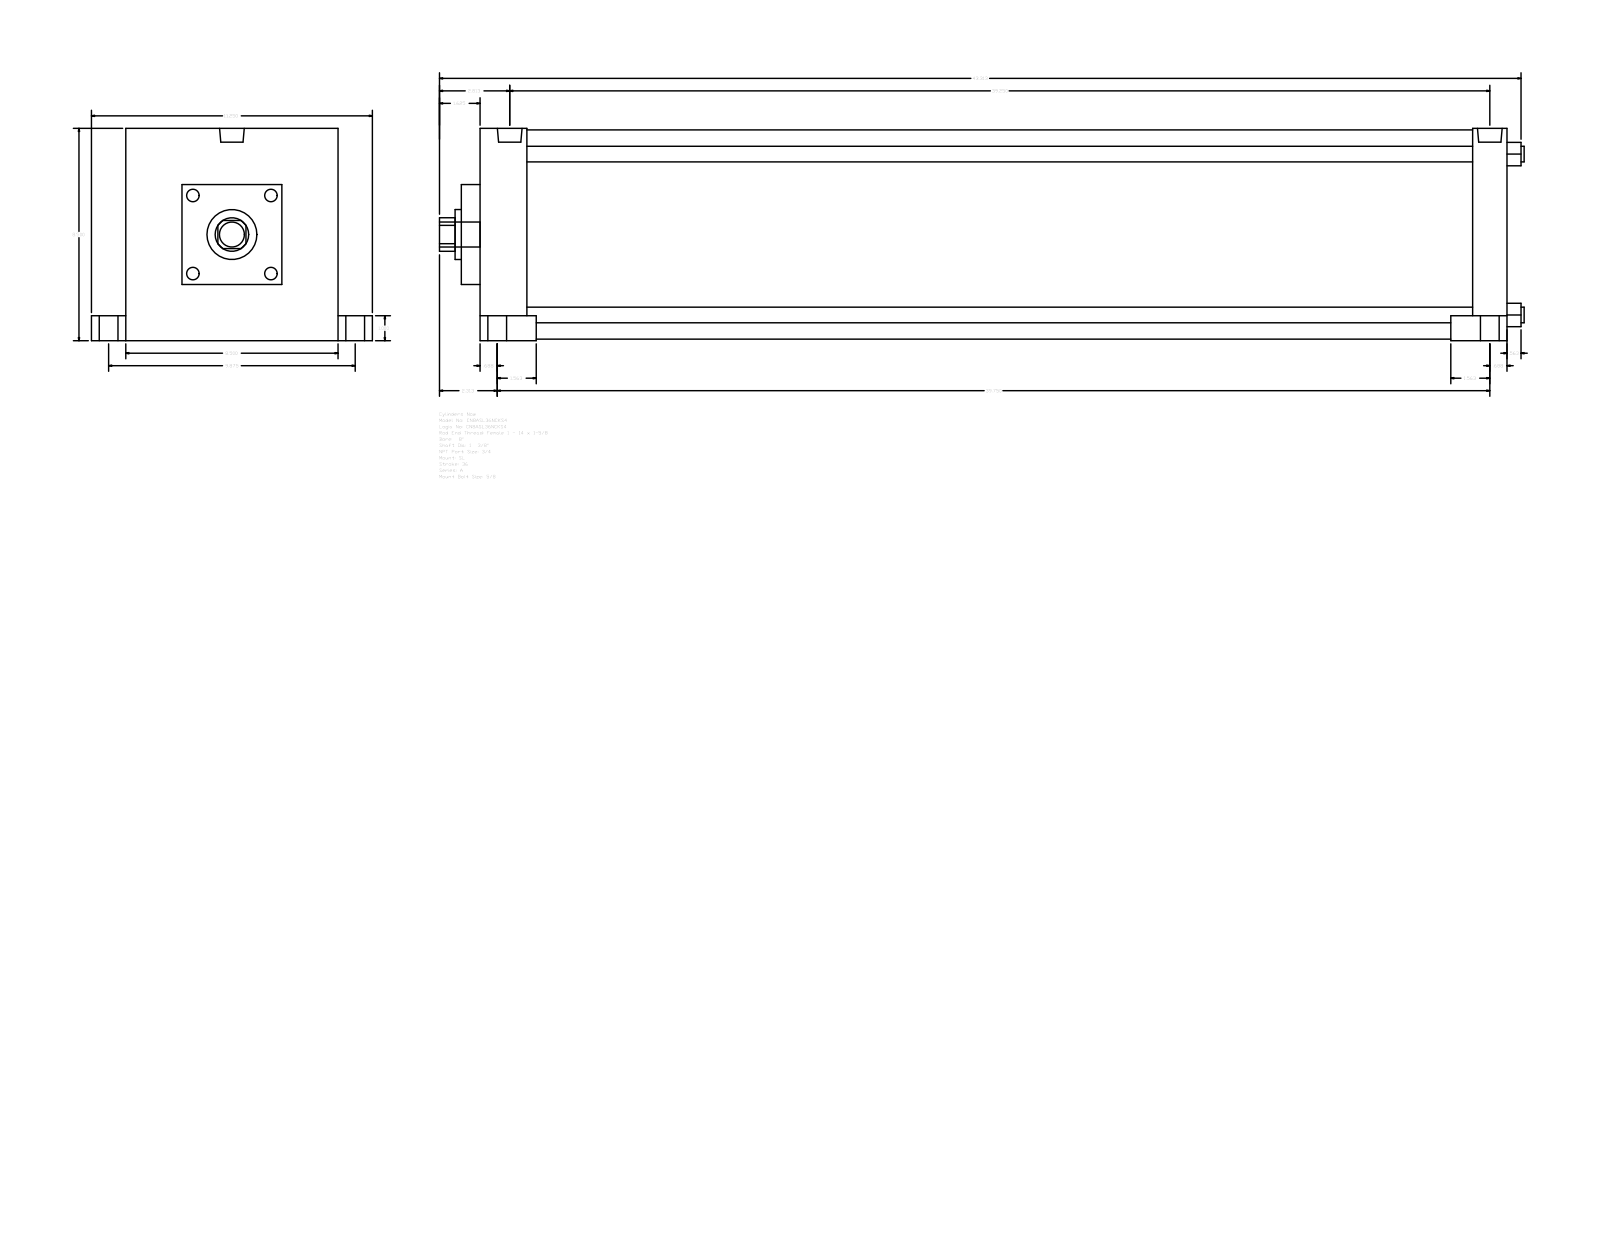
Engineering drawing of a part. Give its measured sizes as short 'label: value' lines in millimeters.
name: A_SL__0800_1.375
written by: GSSL Pune (CONFIG_CONTROL_DESIGN)
unit: mm
bodies: 0 solids, 117 faces (85 planar, 32 cylindrical, 0 other)
size: 1103.31 × 285.75 × 215.9
holes: 4× ⌀15.88, 1× ⌀34.92, 1× ⌀50.8, 1× ⌀212.72
bosses: 5× ⌀25.4, 4× ⌀19.05, 4× ⌀15.08, 2× ⌀25.12
rounds: 1× R17.06
face distances: 1044.58, 215.9, 34.93, 57.15, 47.63, 996.95, 1009.65, 962.02, 19.04, 66.67
hole spacings: 115.67, 163.58, 231.34
